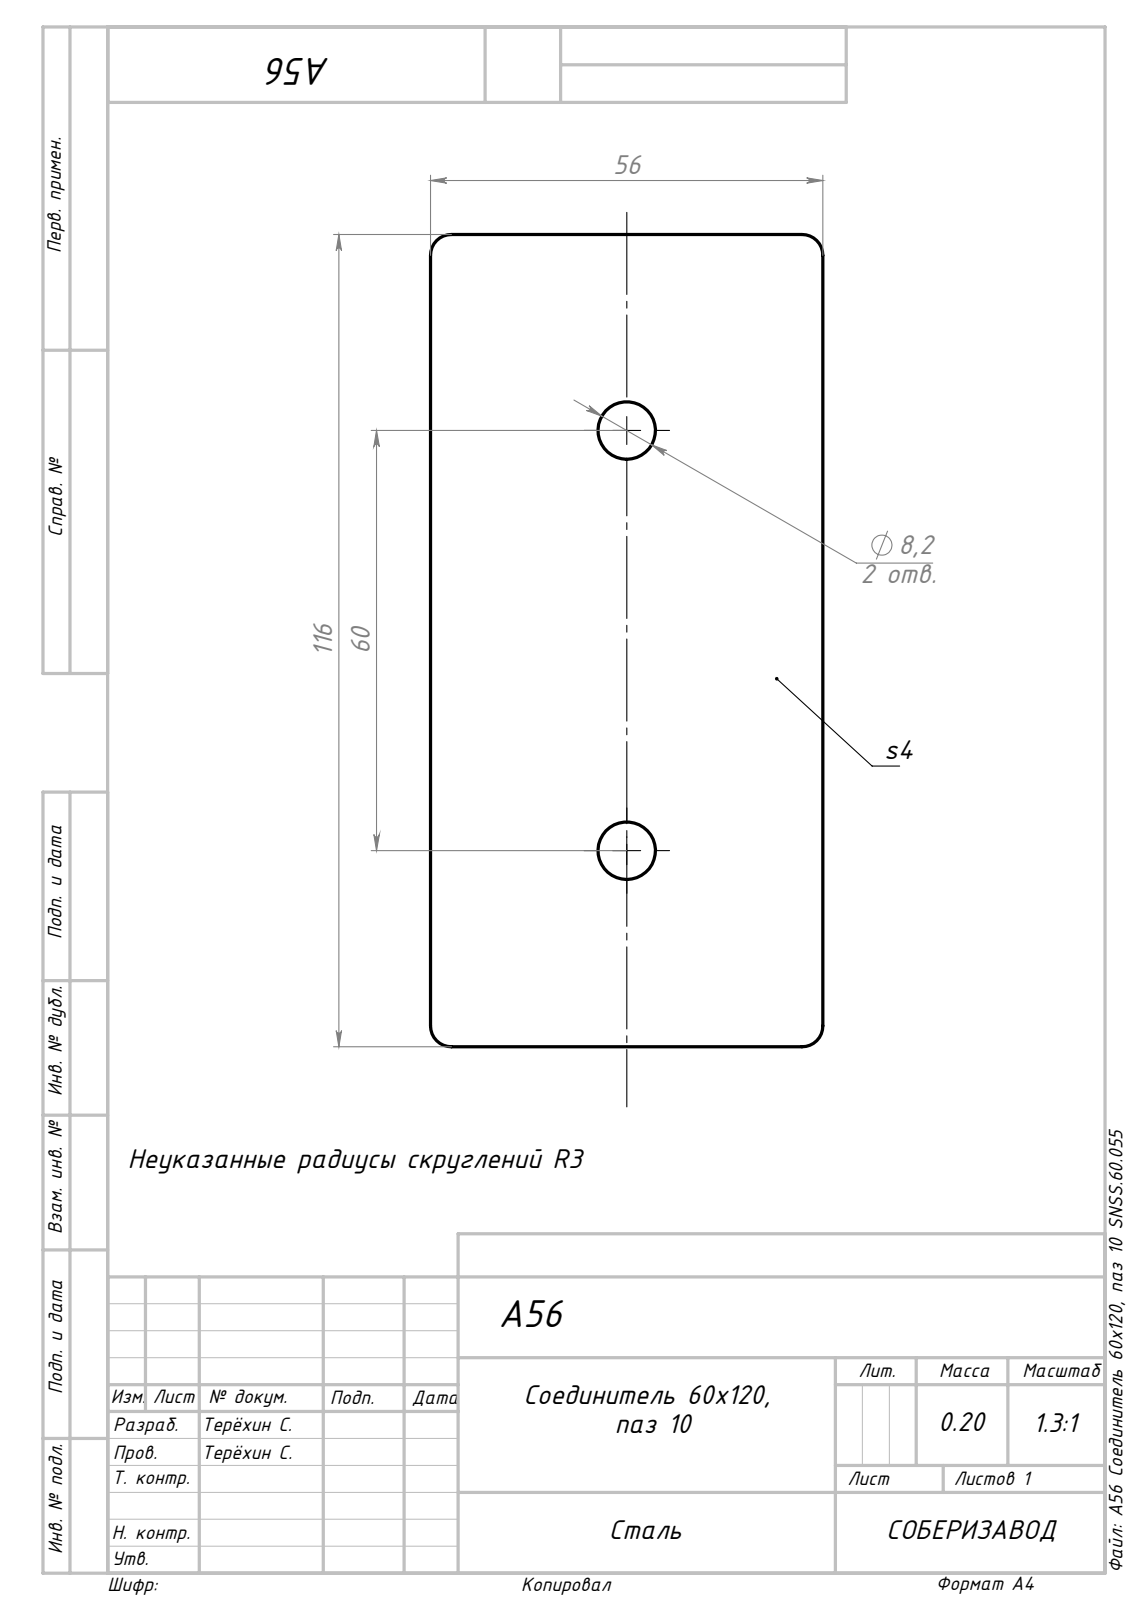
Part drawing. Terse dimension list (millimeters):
name: Сборка1; A56 Cоединитель 60x120, паз 10 SNSS.60.055_00
written by: SolidWorks 2022 (AUTOMOTIVE_DESIGN)
unit: mm
bodies: 1 solid, 14 faces (6 planar, 8 cylindrical, 0 other)
size: 116 × 56 × 4
volume: 25 531 mm³; area: 14 327 mm²
holes: 2× ⌀8.2
rounds: 4× R3
face distances: 4, 56, 116
hole spacings: 60
